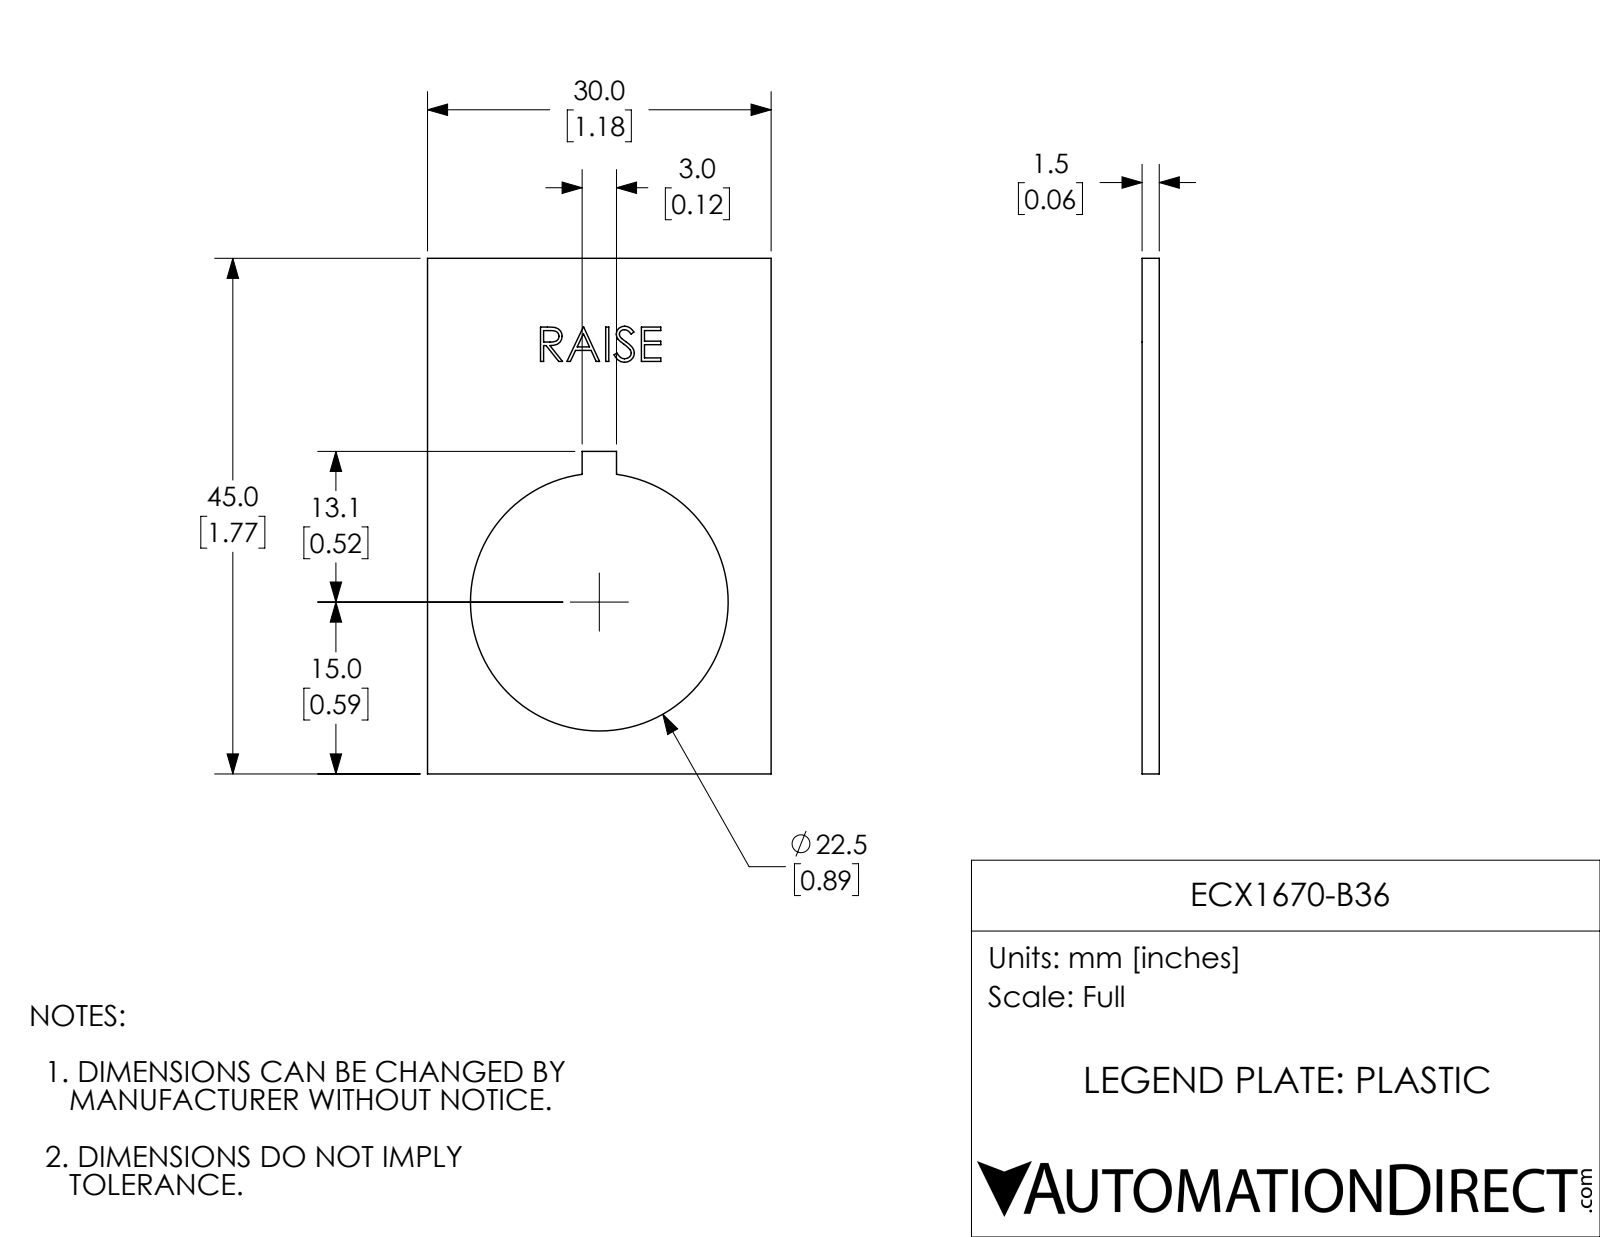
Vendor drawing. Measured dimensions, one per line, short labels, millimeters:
name: ECX1670-B36
written by: SolidWorks 2017 (AUTOMOTIVE_DESIGN)
unit: mm
bodies: 1 solid, 79 faces (56 planar, 3 cylindrical, 20 other)
size: 45 × 30 × 1.5
volume: 1 400 mm³; area: 2 232 mm²
holes: 1× ⌀22.5
face distances: 1.5, 30, 45, 1.5, 13.5, 16.5, 28.1, 16.8, 3, 0.3
